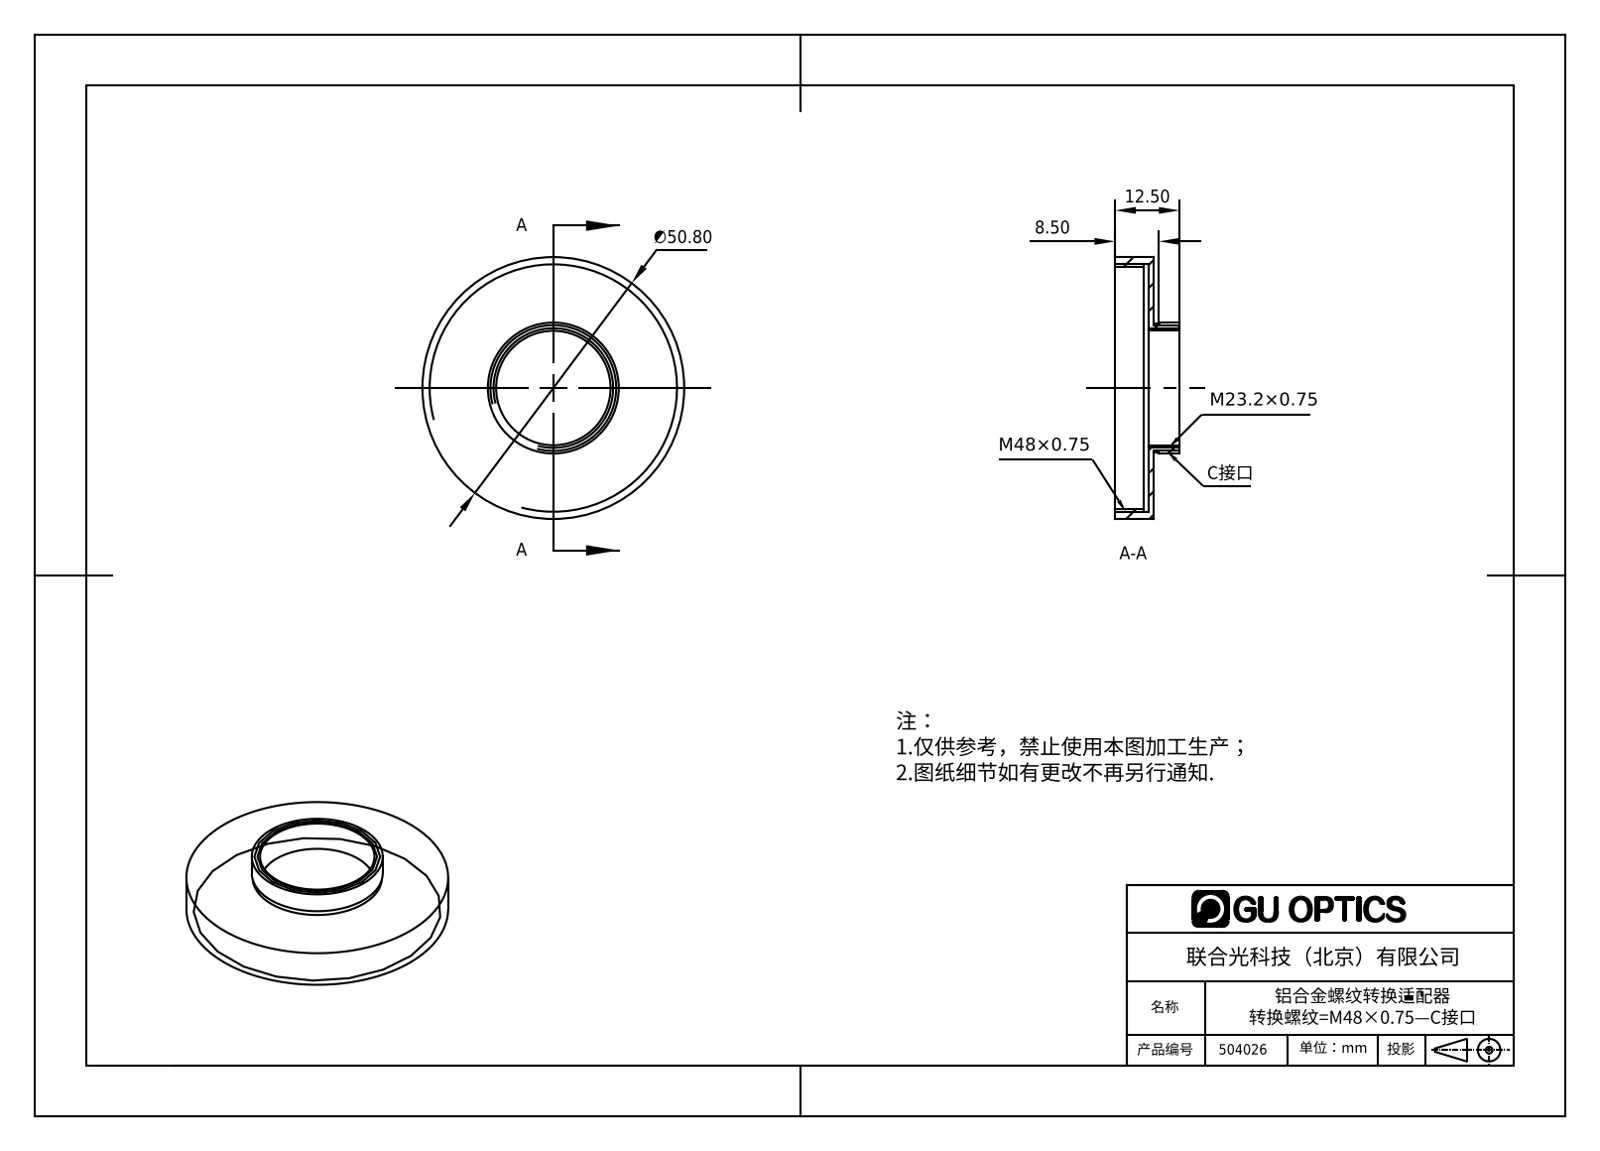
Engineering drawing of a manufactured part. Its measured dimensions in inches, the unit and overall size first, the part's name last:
Units: inches
Overall size (bounding box): 2 × 2 × 0.492
Round holes (diameter × count): ⌀0.874 ×1, ⌀1.85 ×1, ⌀1.898 ×1
Round bosses / shafts (diameter × count): ⌀2 ×1, ⌀1 ×1, ⌀0.988 ×1
Main face-to-face distances: 0.039, 0.256, 0.295, 0.492, 0.236, 0.197, 0.079, 0.217, 0.276, 0.335
Volume: 0.246 in³ · Surface area: 10.01 in²
Bodies: 1 solid, 18 faces (6 planar, 12 cylindrical, 0 other)
Part name (STEP PRODUCT): 504026
STEP written by: SolidWorks 2016 (AUTOMOTIVE_DESIGN)
